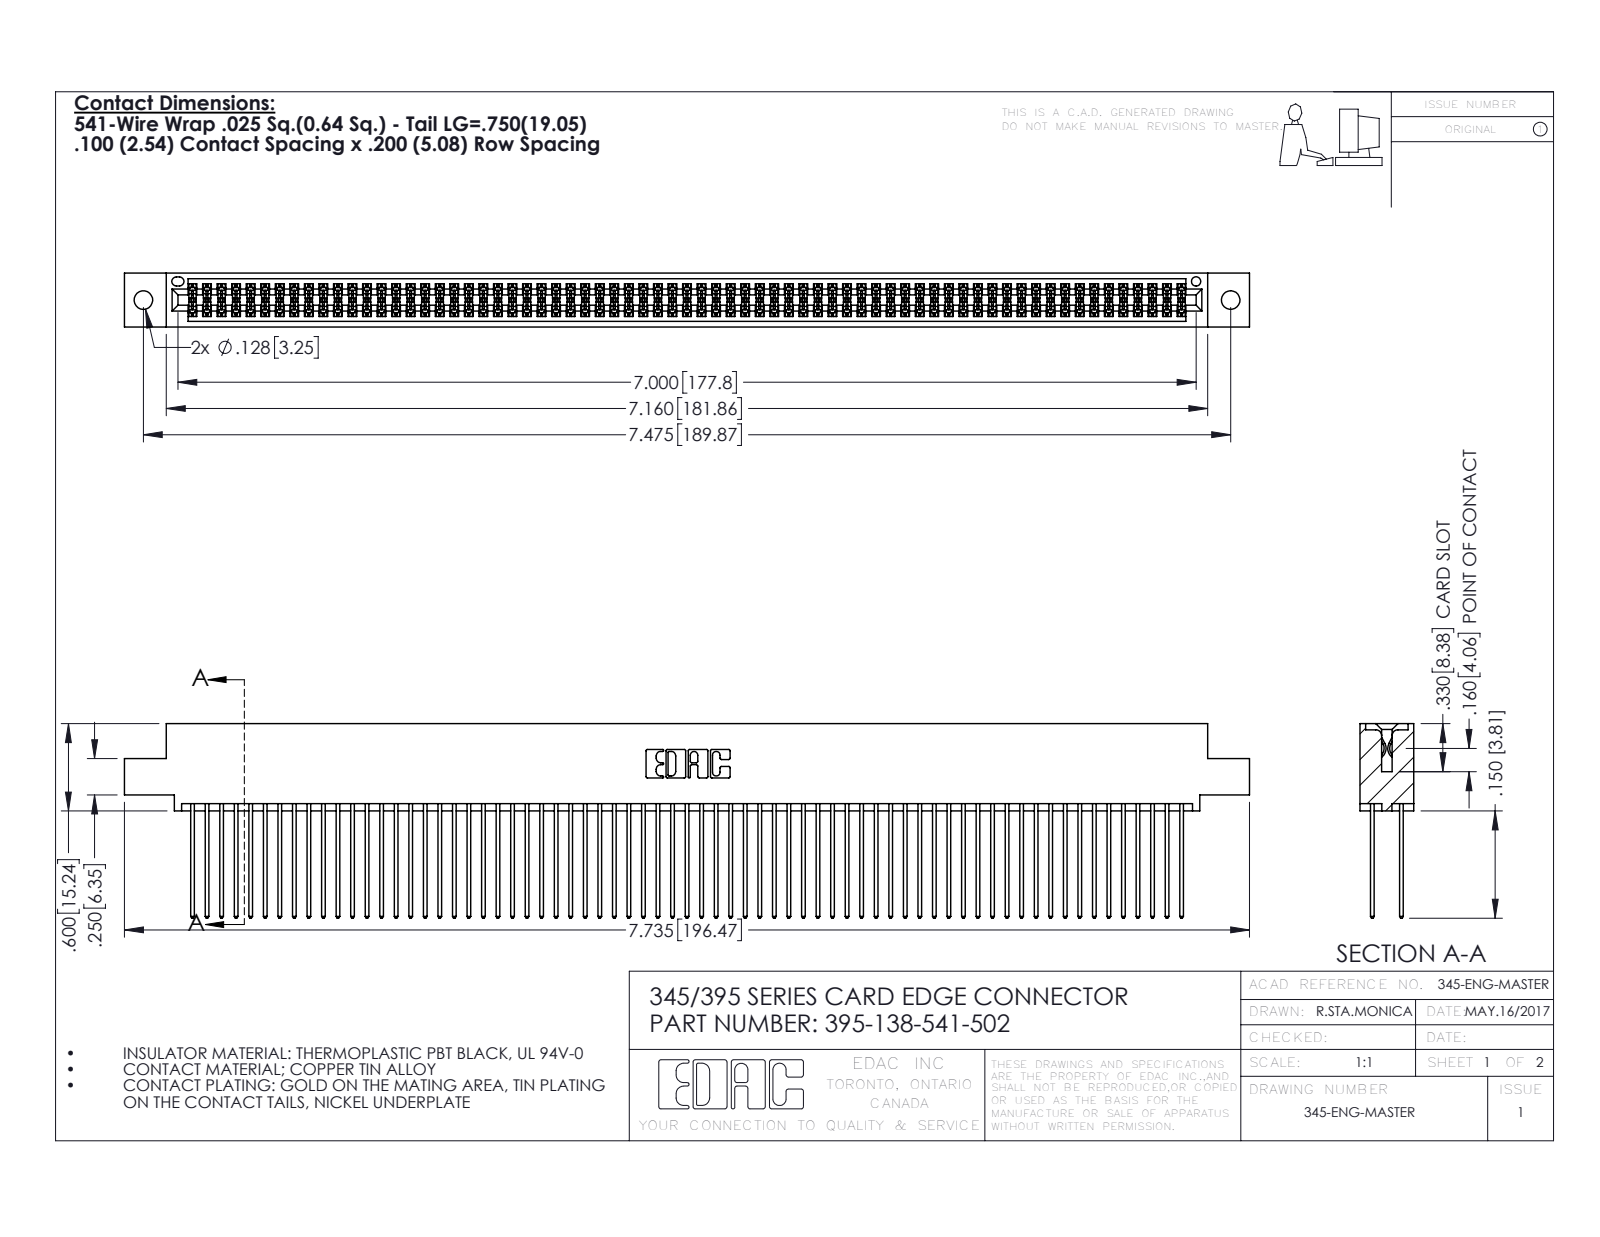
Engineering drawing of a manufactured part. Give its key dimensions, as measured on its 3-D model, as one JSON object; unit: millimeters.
{"part_name": "345 Part_0.110 Offset - 0.128 Dia; 395-138-541-502; 345-292-001_345-293-141", "step_written_by": "SolidWorks 2016 (CONFIG_CONTROL_DESIGN)", "units": "millimeters", "bodies": {"solids": 139, "faces": 7030, "planar": 4638, "cylindrical": 2392, "other": 0}, "overall_size": [196.5, 34, 9.4], "volume_mm3": 20020, "surface_area_mm2": 33650, "round_holes": [[3.3, 2], [1.6, 1]], "partial_cylinders_radius": [[0.2, 207], [0.3, 138], [0.3, 22], [0.2, 6], [0.8, 6], [0.7, 3], [0.4, 2], [0.5, 2]], "face_to_face_distances": [1.8, 7.6, 5.1, 2.5, 6.9, 0.6, 5.7, 9.4, 4.4, 3.8], "hole_center_spacings": [6.9, 183.9, 189.9]}
